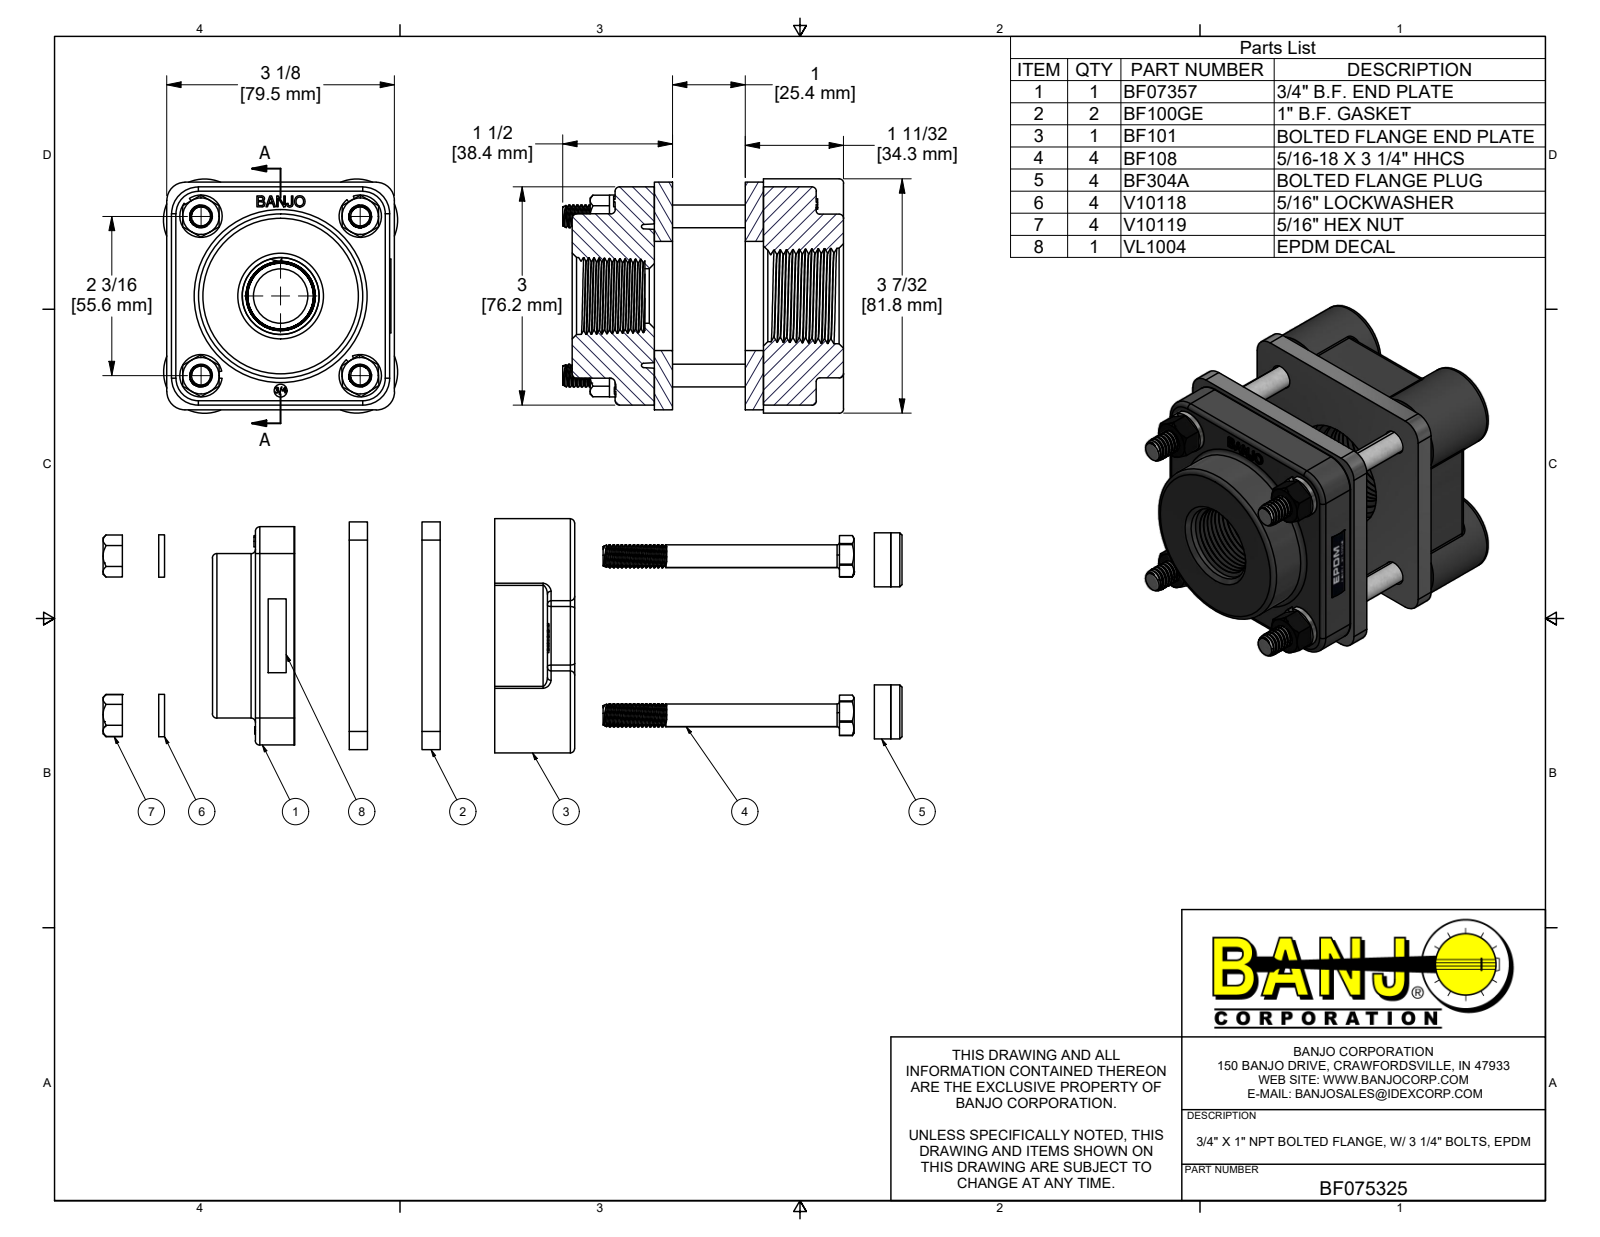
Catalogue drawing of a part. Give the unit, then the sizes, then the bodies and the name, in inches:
Units: inches
Overall size (bounding box): 17.244 × 3.22 × 3.22
Round holes (diameter × count): ⌀0.252 ×4, ⌀0.313 ×4, ⌀0.322 ×4, ⌀0.34 ×4, ⌀0.344 ×4, ⌀0.35 ×4, ⌀0.72 ×4, ⌀0.745 ×4, ⌀0.18 ×1, ⌀0.75 ×1, ⌀1.5 ×1
Round bosses / shafts (diameter × count): ⌀0.268 ×60, ⌀0.742 ×4, ⌀0.583 ×4, ⌀0.313 ×4, ⌀2.26 ×1
Partial cylindrical surfaces — rounded edges, fillets, slot ends (radius × count): R0.06 ×20, R0.05 ×8, R0.134 ×8, R0.25 ×4, R0.284 ×4, R0.37 ×4, R0.565 ×4, R0.315 ×1
Main face-to-face distances: 0.25, 1.25, 1.5, 1.1, 2.6, 1.35, 0.54, 1.79, 2.04, 3.14
Hole centre spacings: 2.139, 2.196, 2.142, 2.146, 2.19, 2.194, 0.069, 1.55
Volume: 17.19 in³ · Surface area: 288.6 in²
Bodies: 20 solids, 1622 faces (512 planar, 443 cylindrical, 667 other)
Part name (STEP PRODUCT): BF075325; BF101; BF07357; V07357X (+6 more)
STEP written by: Autodesk Inventor 2019 (AUTOMOTIVE_DESIGN)
